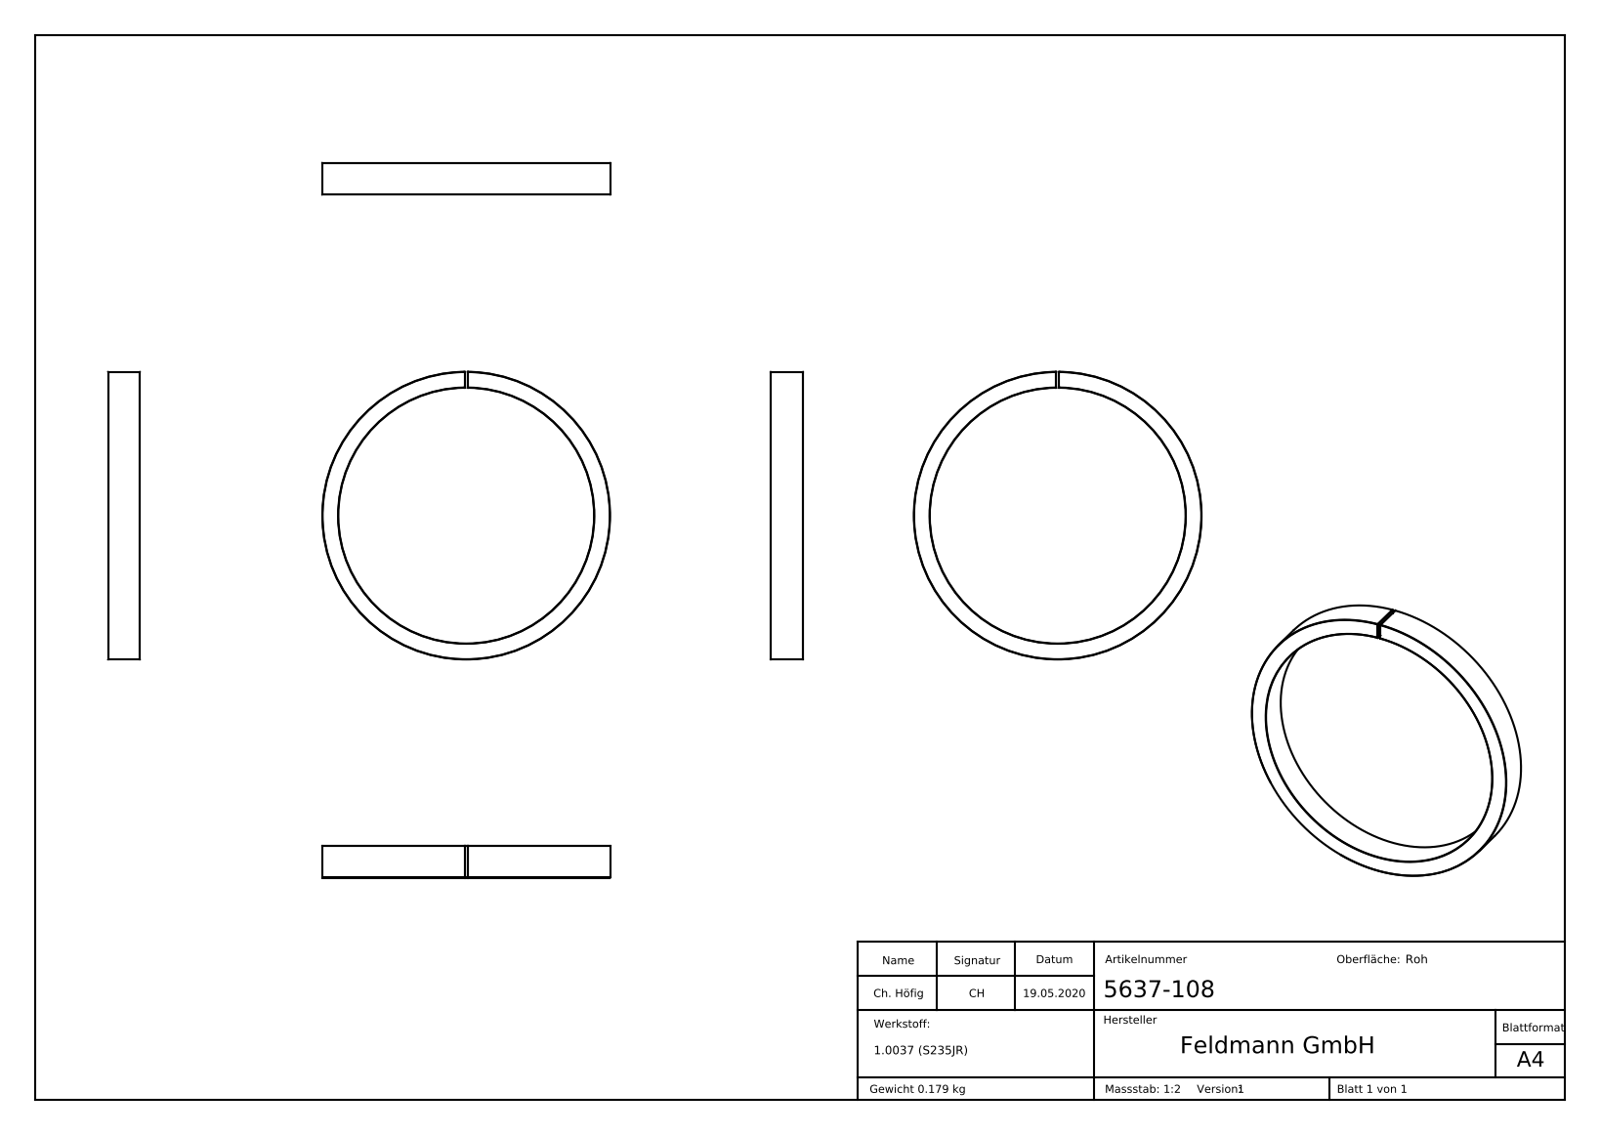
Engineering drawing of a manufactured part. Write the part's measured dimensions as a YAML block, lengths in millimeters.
part_name: "5637-108"
step_written_by: "SolidWorks 2015 (CONFIG_CONTROL_DESIGN)"
units: millimeters
bodies: {solids: 1, faces: 216, planar: 109, cylindrical: 2, other: 105}
overall_size: [108, 108, 12]
volume: 23000
surface_area: 11649
round_holes:
  - {diameter: 96, count: 1}
round_bosses_or_shafts:
  - {diameter: 108, count: 1}
face_to_face_distances: [12, 1, 1.1, 1.78, 0.83, 2.12, 2.45, 0.99, 2.77, 1.21]
